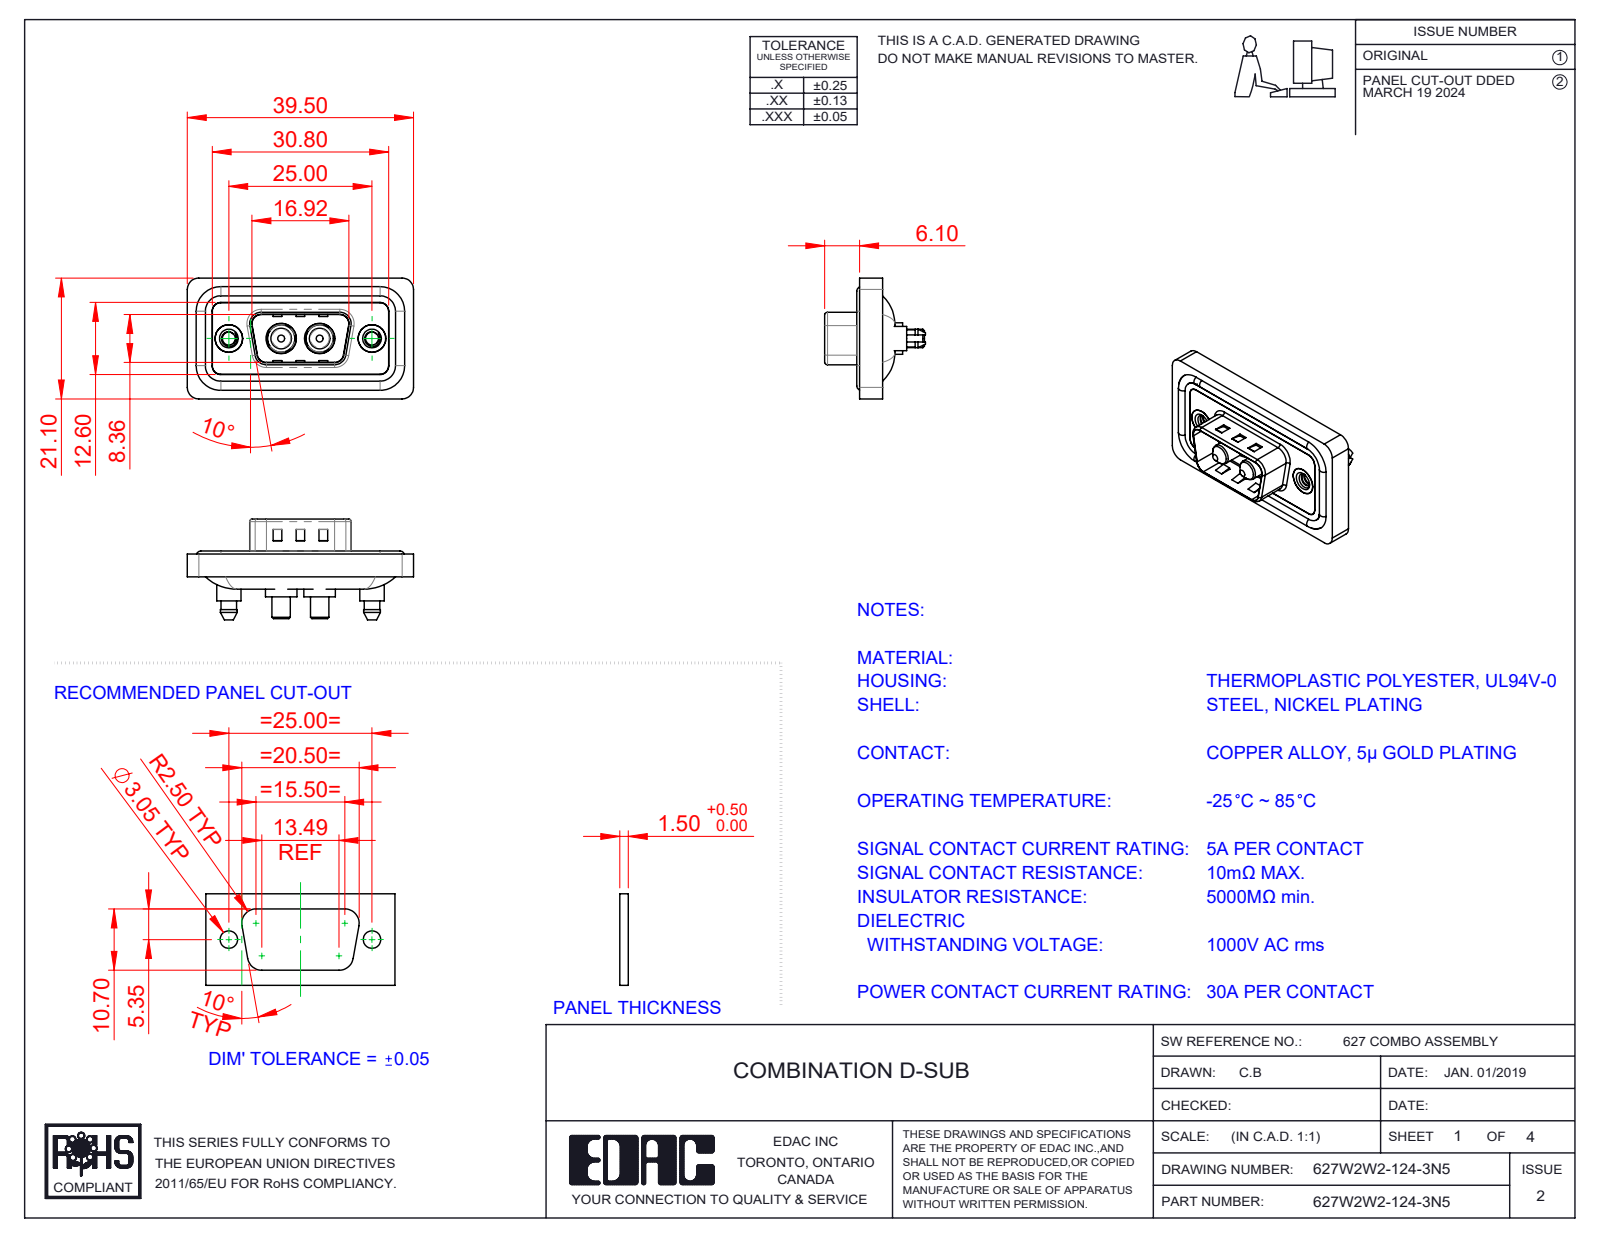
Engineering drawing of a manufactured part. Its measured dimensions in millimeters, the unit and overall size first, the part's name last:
Units: millimetres
Overall size (bounding box): 39.5 × 21.1 × 17.6
Round holes (diameter × count): ⌀2.26 ×2, ⌀4 ×2, ⌀4.8 ×2, ⌀4.85 ×2, ⌀5 ×2, ⌀5.3 ×2
Round bosses / shafts (diameter × count): ⌀1.6 ×4, ⌀5.5 ×2, ⌀5.4 ×2, ⌀5.2 ×2, ⌀4.9 ×2, ⌀4.75 ×2, ⌀4.25 ×2, ⌀3.75 ×2
Partial cylindrical surfaces — rounded edges, fillets, slot ends (radius × count): R1.5 ×24, R2 ×18, R1.6 ×10, R0.5 ×8, R0.25 ×4, R0.6 ×4, R0.65 ×4, R0.9 ×4
Main face-to-face distances: 0.4, 1.1, 2.9, 3.1, 0.5, 1.6, 1.5, 4, 0.7, 2.5
Hole centre spacings: 9.14, 15.86, 6.72, 25
Volume: 4 608 mm³ · Surface area: 7 326 mm²
Bodies: 11 solids, 539 faces (181 planar, 250 cylindrical, 108 other)
Part name (STEP PRODUCT): 627Combo Shell Front_09 Contacts; Power Pin_30A S; 627W2W2-124-3N5; 627Combo Threaded Boardlock_5 (+3 more)
STEP written by: SolidWorks 2023 (CONFIG_CONTROL_DESIGN)
